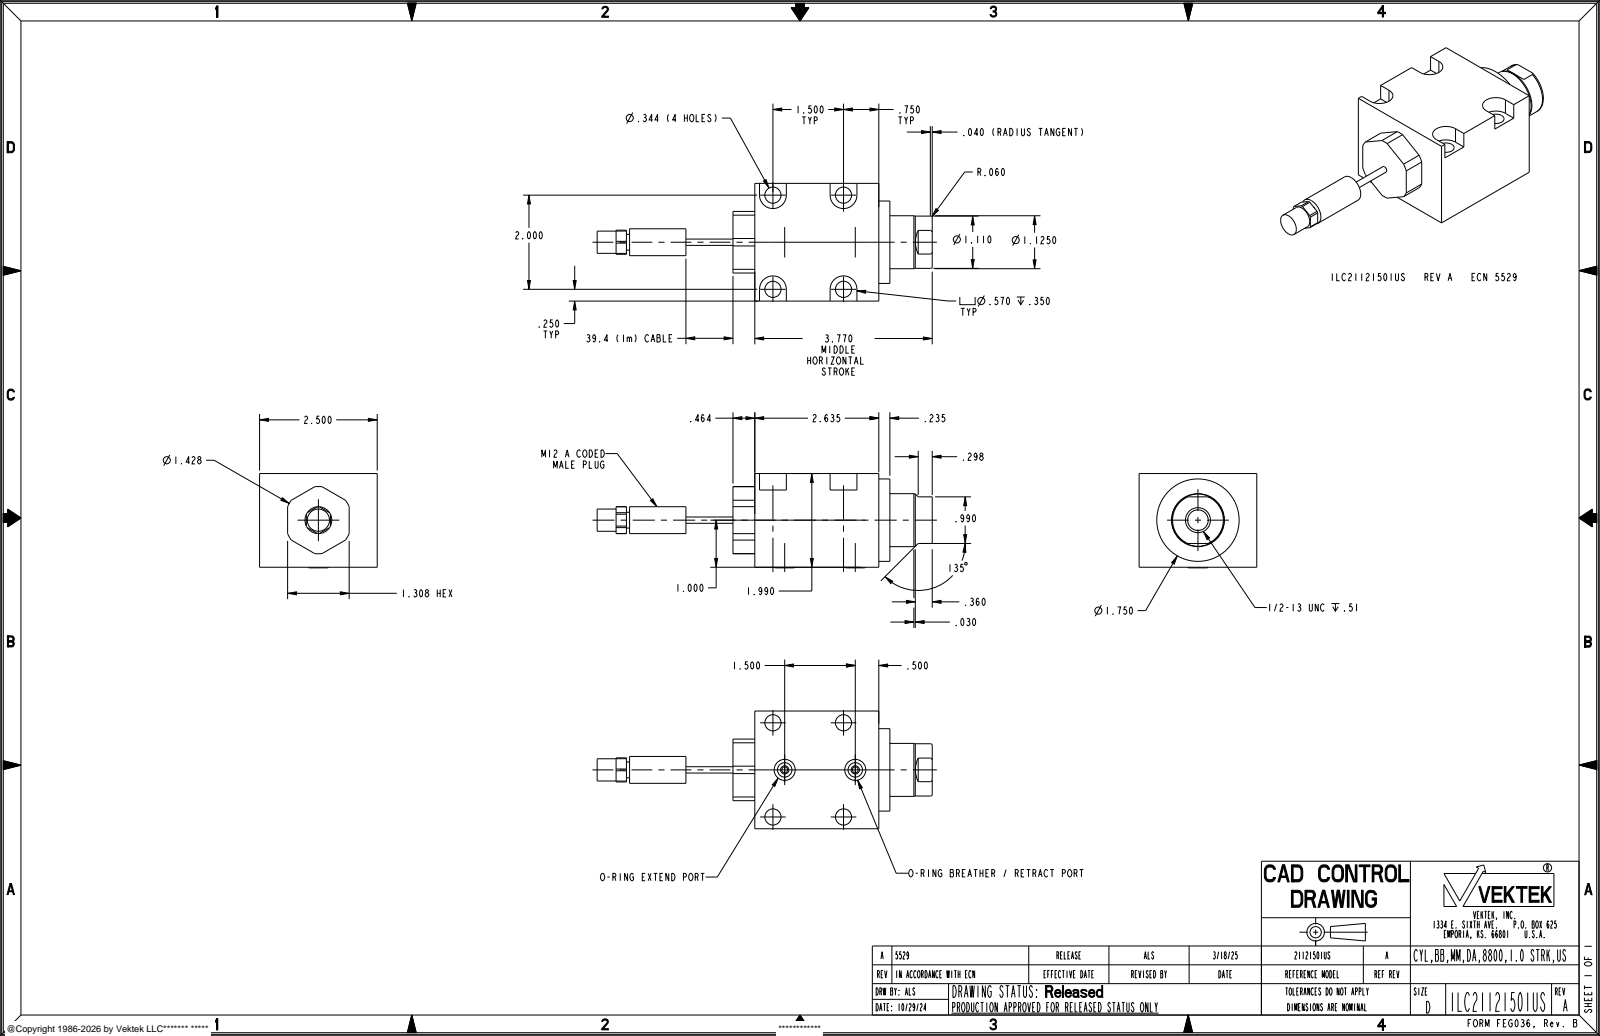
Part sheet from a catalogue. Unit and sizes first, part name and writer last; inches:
Units: inches
Overall size (bounding box): 7.12 × 2.7 × 2.003
Round holes (diameter × count): ⌀0.344 ×4, ⌀0.125 ×2, ⌀0.447 ×2, ⌀0.437 ×1
Round bosses / shafts (diameter × count): ⌀1.75 ×1, ⌀1.125 ×1, ⌀1.11 ×1, ⌀0.571 ×1, ⌀0.5 ×1, ⌀0.472 ×1, ⌀0.335 ×1, ⌀0.134 ×1
Partial cylindrical surfaces — rounded edges, fillets, slot ends (radius × count): R0.285 ×4, R0.714 ×1
Main face-to-face distances: 1.99, 2.5, 2.635, 3.099, 0.464, 0.235, 2.87, 3.334, 1.135, 1.308
Hole centre spacings: 1.031, 1.5, 1.601, 2, 2.016, 2.5
Volume: 14.56 in³ · Surface area: 54.49 in²
Bodies: 1 solid, 120 faces (46 planar, 52 cylindrical, 22 other)
Part name (STEP PRODUCT): ILC21121501US
STEP written by: CREO PARAMETRIC BY PTC INC, 2021164 (AUTOMOTIVE_DESIGN)
